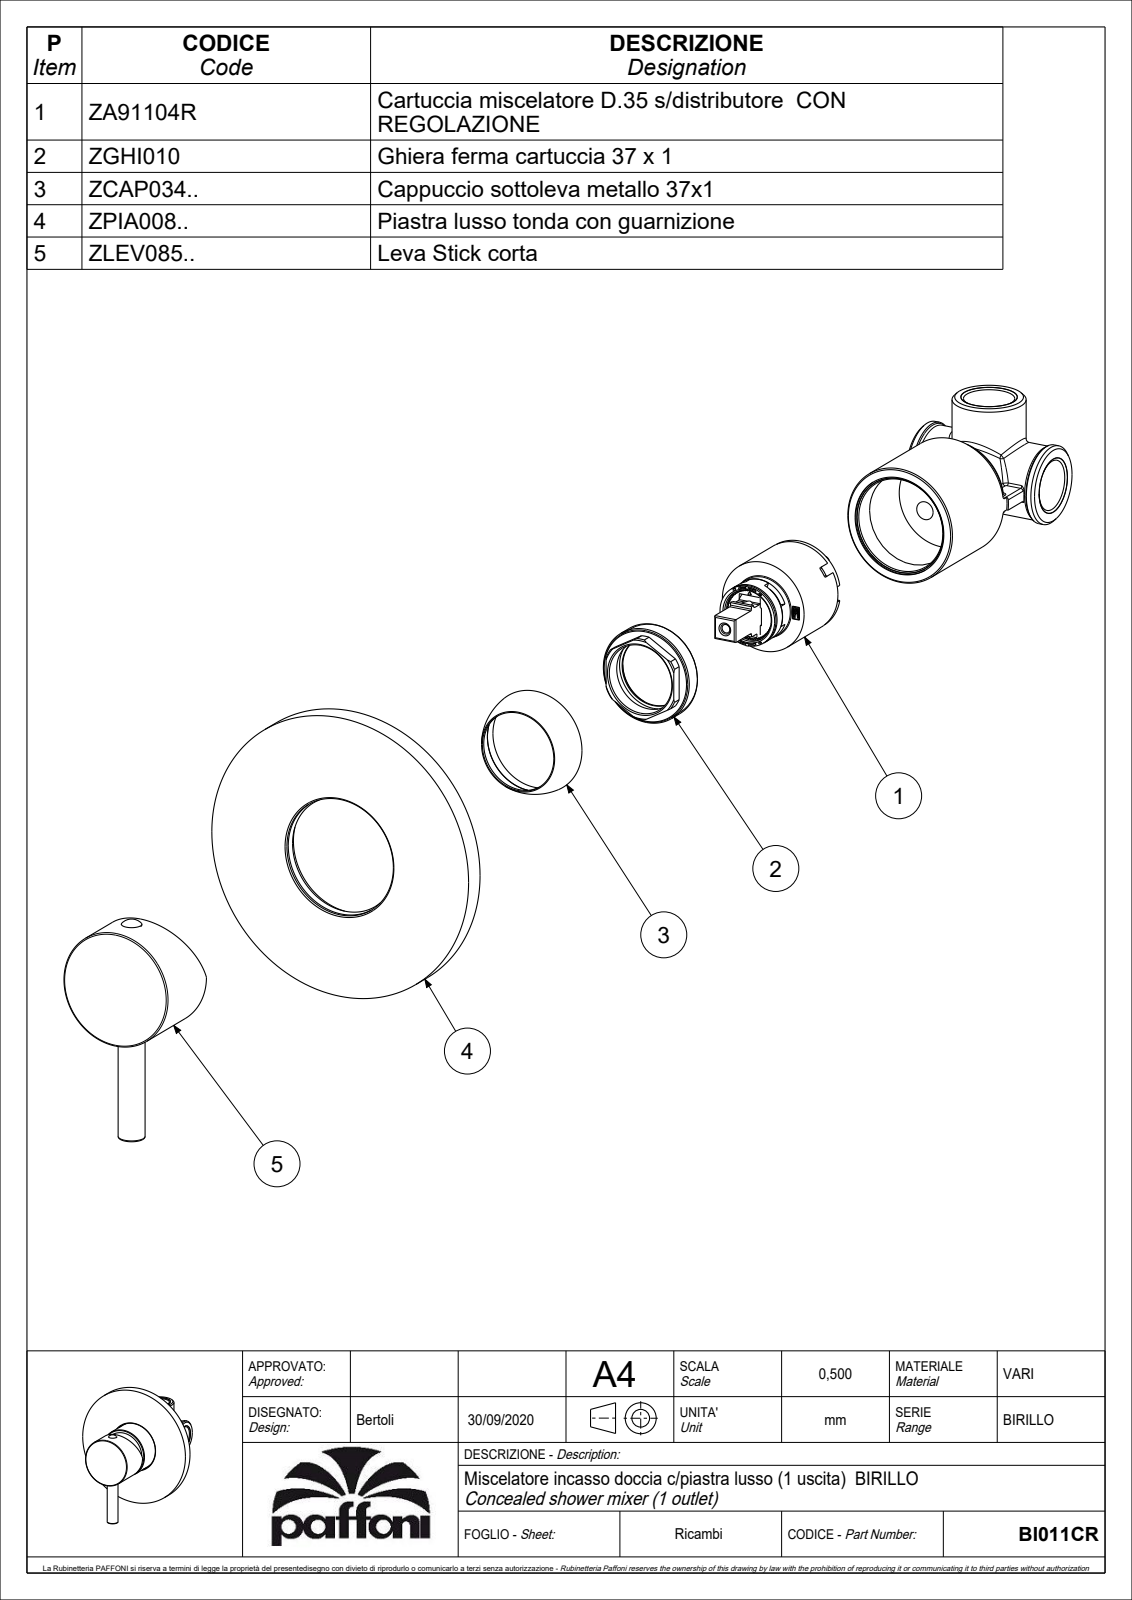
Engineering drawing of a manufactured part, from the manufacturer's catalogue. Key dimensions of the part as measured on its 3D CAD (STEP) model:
Part name (STEP PRODUCT): BI011CR
STEP written by: CREO PARAMETRIC BY PTC INC, 2020044 (CONFIG_CONTROL_DESIGN)
Units: millimetres
Bodies: 2 solids, 987 faces (577 planar, 224 cylindrical, 186 other)
Overall size (bounding box): 117 × 110 × 60.69
Volume: 72 065 mm³ · Surface area: 61 640 mm²
Round holes (diameter × count): ⌀4 ×2, ⌀3 ×1, ⌀3.3 ×1, ⌀5 ×1, ⌀5.5 ×1, ⌀19.5 ×1, ⌀19.9 ×1, ⌀26.8 ×1, ⌀29 ×1, ⌀31 ×1, ⌀32.4 ×1, ⌀36 ×1
Round bosses / shafts (diameter × count): ⌀110 ×1, ⌀54.6 ×1, ⌀44.8 ×1, ⌀44.5 ×1, ⌀35 ×1, ⌀32.2 ×1, ⌀23.5 ×1, ⌀23.4 ×1
Partial cylindrical surfaces — rounded edges, fillets, slot ends (radius × count): R0.5 ×35, R0.15 ×11, R0.3 ×4, R1 ×2, R7 ×1, R9.3 ×1, R10.85 ×1, R11.25 ×1
Main face-to-face distances: 7, 1.5, 5.5, 21.5, 2.3, 4.7, 56.3, 54, 49.3, 20.7
Hole centre spacings: 11.7
